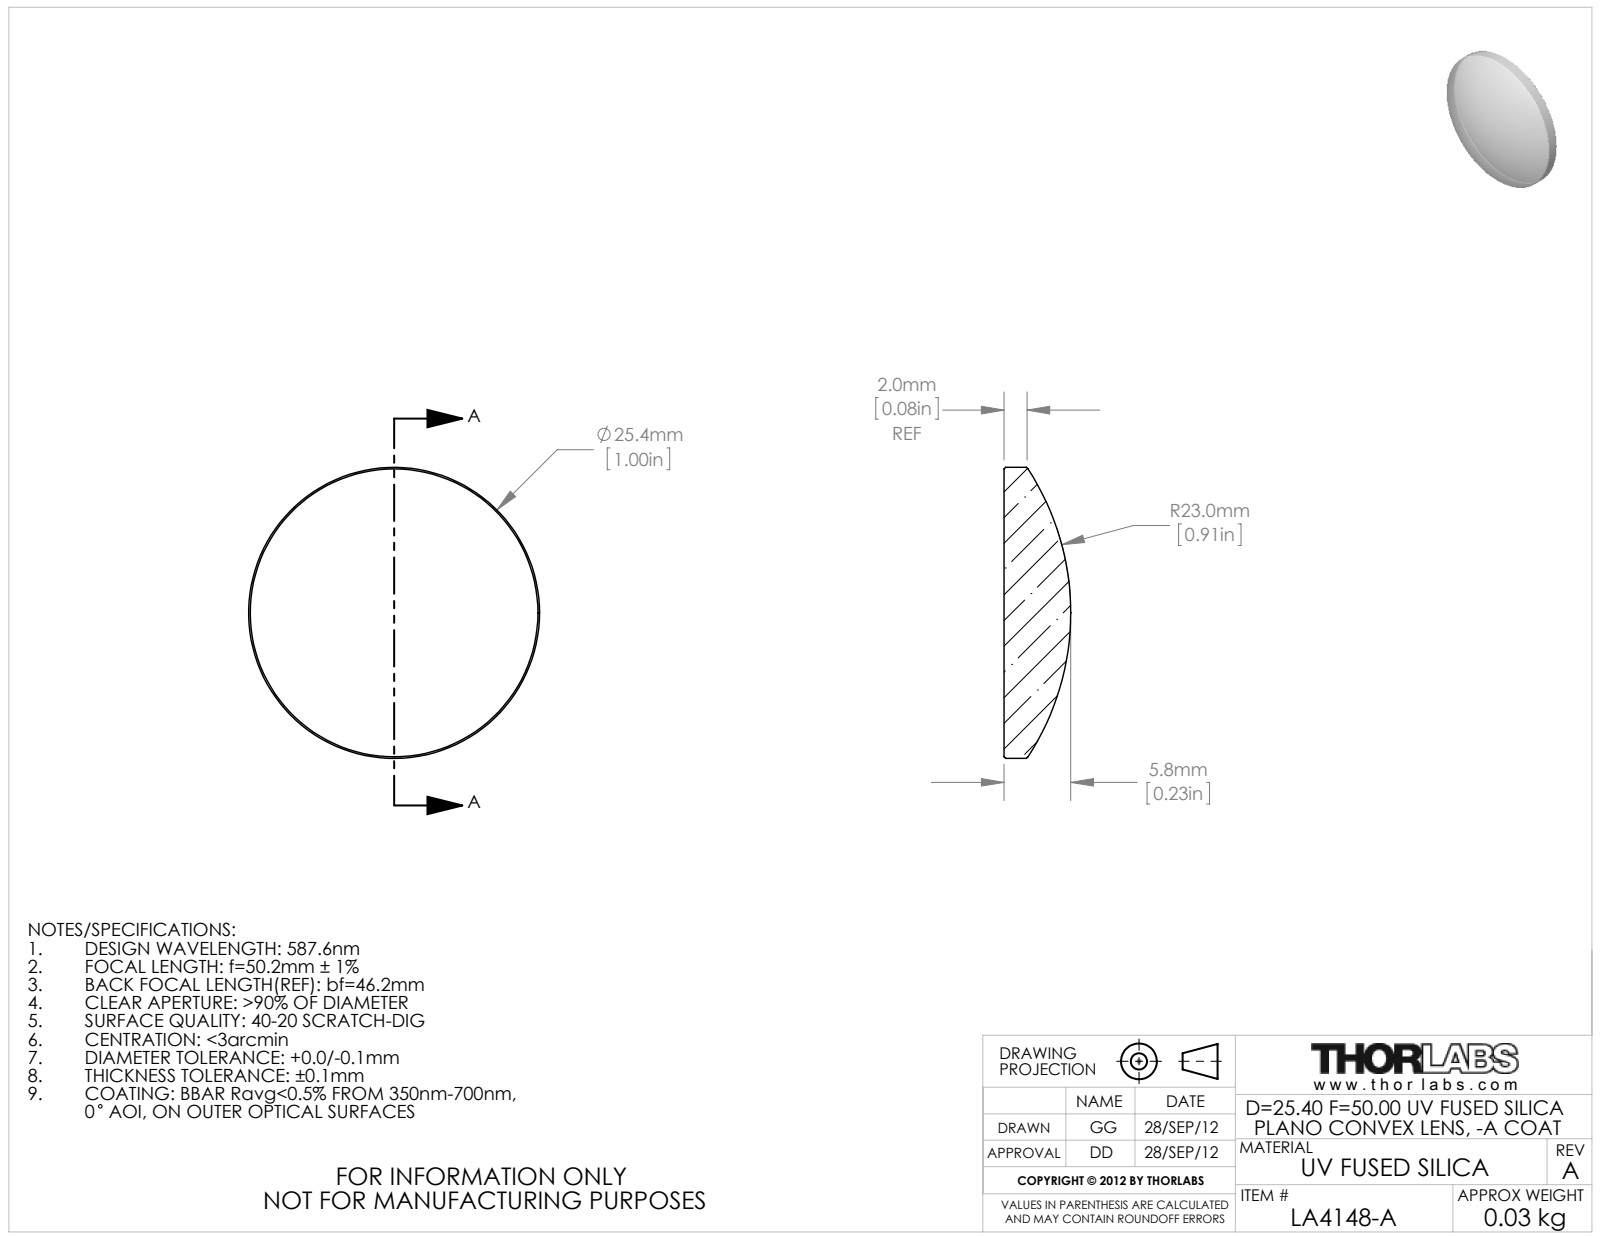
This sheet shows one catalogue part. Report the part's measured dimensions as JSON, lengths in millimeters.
{"part_name": "24972-E0W", "step_written_by": "SolidWorks 2011 (CONFIG_CONTROL_DESIGN)", "units": "millimeters", "bodies": {"solids": 1, "faces": 9, "planar": 1, "cylindrical": 2, "other": 6}, "overall_size": [25.4, 25.4, 5.82], "volume_mm3": 2010, "surface_area_mm2": 1211, "round_bosses_or_shafts": [[25.4, 1]]}
